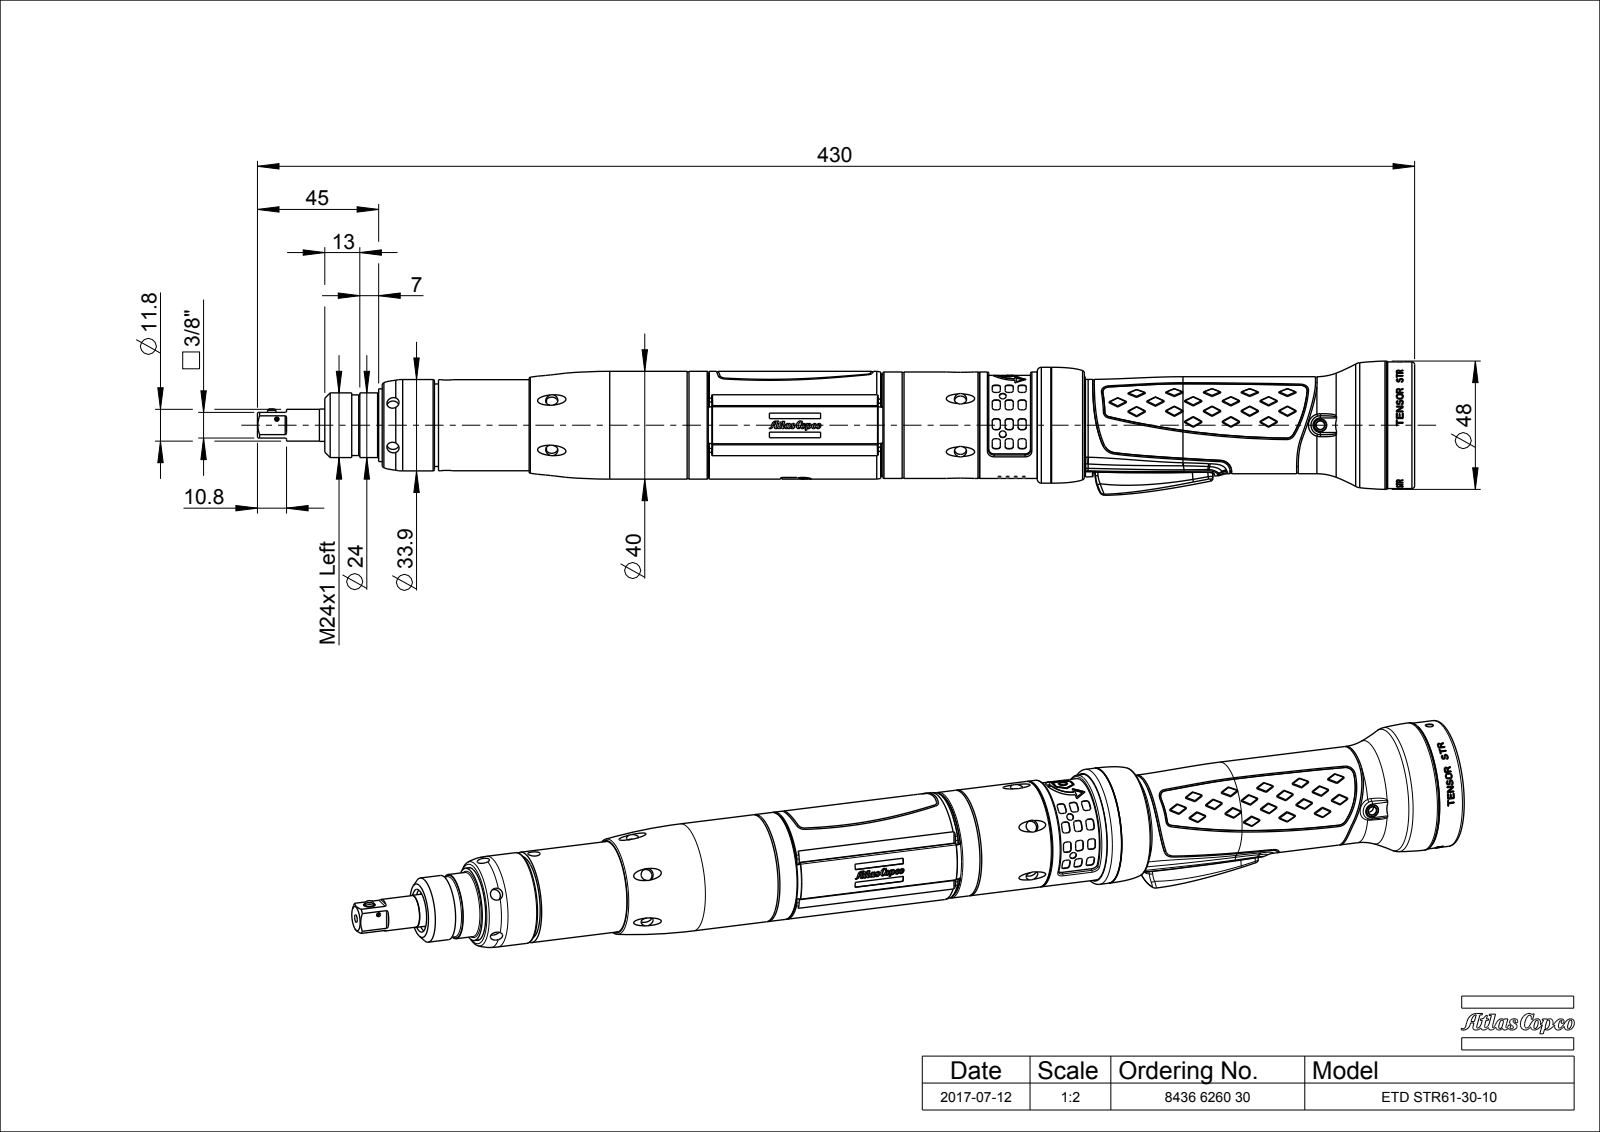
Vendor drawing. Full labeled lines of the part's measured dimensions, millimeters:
Part name (STEP PRODUCT): 4220502200; 4220435380-MONTERAD_ASM; 4220474480_ASM; 4220474580_ASM (+8 more)
STEP written by: PRO/ENGINEER BY PARAMETRIC TECHNOLOGY CORPORATION, 2013410 (CONFIG_CONTROL_DESIGN)
Units: millimetres
Bodies: 37 solids, 8724 faces (4432 planar, 1418 cylindrical, 2874 other)
Overall size (bounding box): 429.59 × 49.81 × 47.62
Volume: 147 141 mm³ · Surface area: 162 869 mm²
Round holes (diameter × count): ⌀1 ×13, ⌀2.67 ×12, ⌀3.31 ×12, ⌀3.6 ×10, ⌀4.5 ×10, ⌀0.6 ×9, ⌀0.8 ×5, ⌀1.7 ×5, ⌀1.72 ×4, ⌀2.6 ×4, ⌀1.6 ×2, ⌀3.2 ×2
Round bosses / shafts (diameter × count): ⌀3.06 ×9, ⌀2.55 ×9, ⌀2.45 ×9, ⌀2.25 ×9, ⌀1.56 ×9, ⌀2.63 ×5, ⌀1.6 ×5, ⌀2.31 ×4
Partial cylindrical surfaces — rounded edges, fillets, slot ends (radius × count): R0.2 ×141, R0.5 ×77, R2 ×24, R1.12 ×18, R1.23 ×18, R0.25 ×13, R0.3 ×13, R1.5 ×11
Main face-to-face distances: 0.87, 32.03, 37.7, 32.9, 33.76, 199.83, 31.16, 138.6, 338.43, 2.5
Hole centre spacings: 3, 6, 4.48, 7.75, 4.4, 4.5, 15, 21.21
